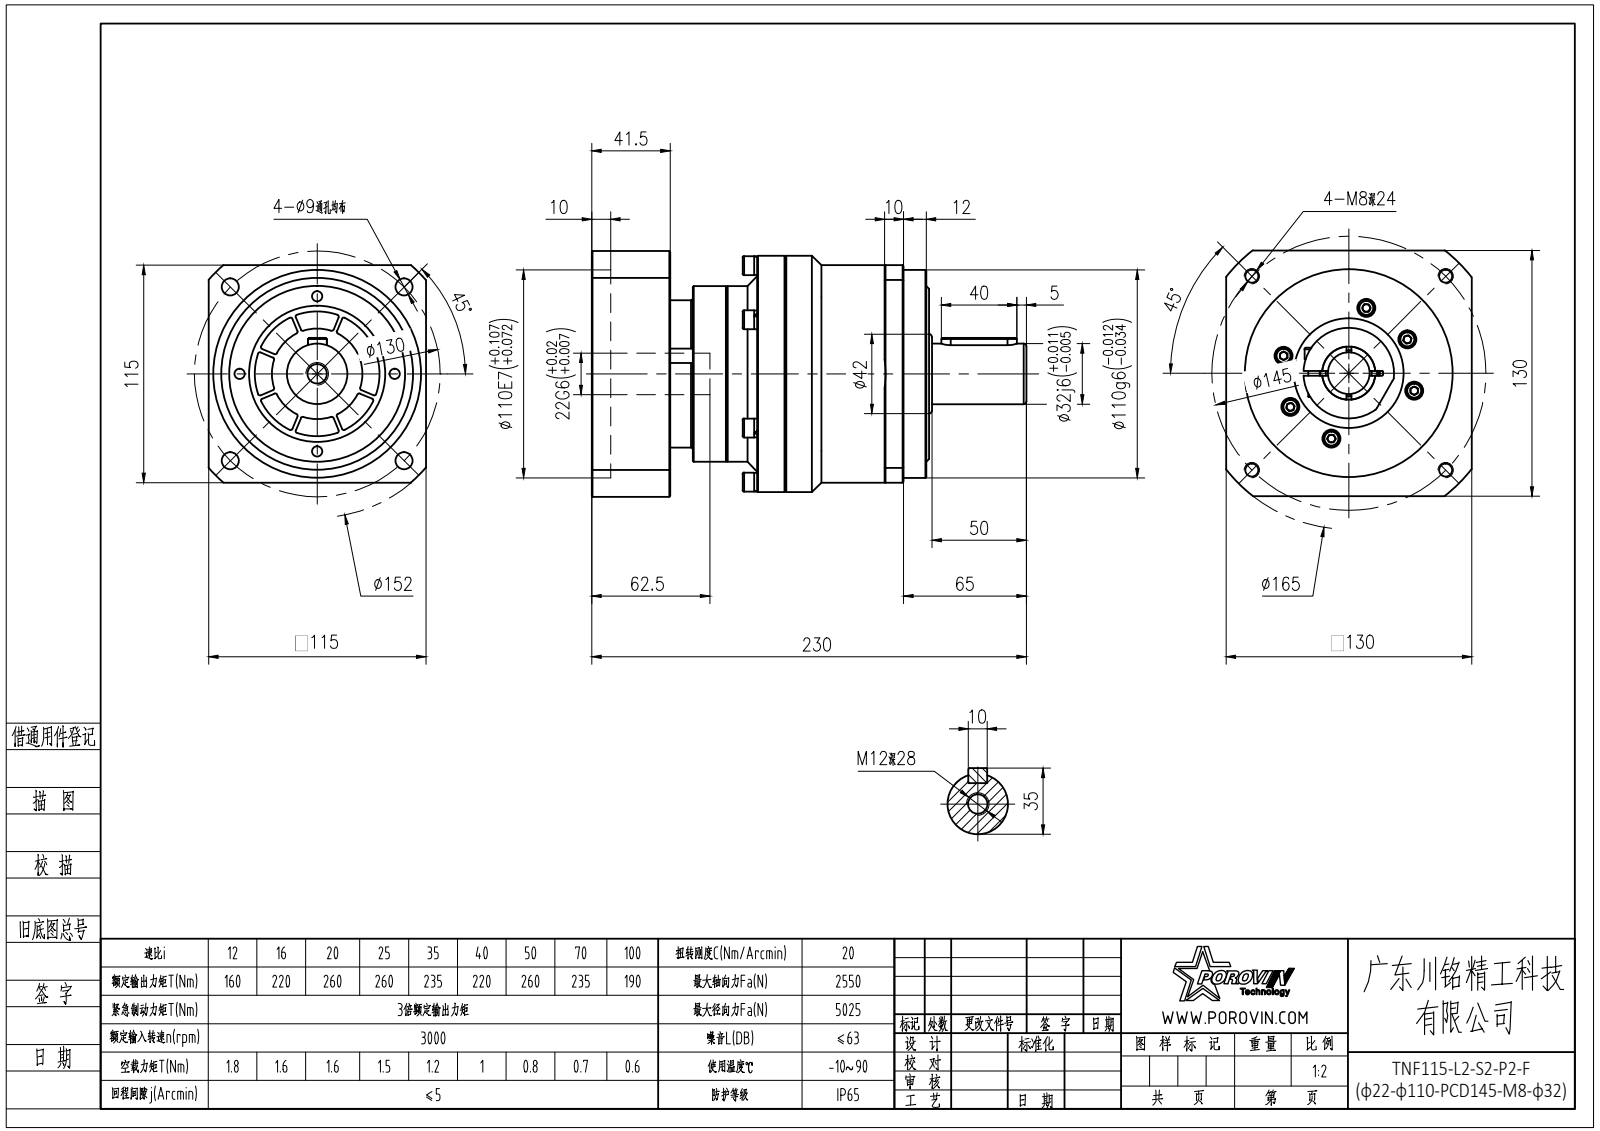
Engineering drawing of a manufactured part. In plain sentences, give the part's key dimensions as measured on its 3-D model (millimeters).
The part is named "hexagon socket head cap screws gb_GB_FASTENER_SCREWS_HSHCS M6X20-N; 一级齿圈加出轴 KS115 外形图; spring lock washers--normal type gb_GB_FASTENER_WASHER_SW 6; hexagon socket head cap screws gb_GB_FASTENER_SCREWS_HSHCS M6X25-N (+4 more)". Its 3-D file was written by "SolidWorks 2016 (CONFIG_CONTROL_DESIGN)". It is 41 solids with 1135 faces: 472 planar, 412 cylindrical and 251 other. Overall it measures 230 by 130 by 130 millimeters. Its volume is 1 633 000 cubic millimeters and its surface area 228 304 square millimeters. Round holes: 14 of diameter 5.5, 12 of diameter 4.2, 10 of diameter 5.4, 10 of diameter 9.5, 6 of diameter 6.6, 6 of diameter 6.68, 4 of diameter 6.8, 4 of diameter 9, 2 of diameter 10.2, 1 of diameter 5, 1 of diameter 6.5, 1 of diameter 13. Round bosses or shafts: 10 of diameter 8.5, 10 of diameter 8, 10 of diameter 5, 7 of diameter 10, 7 of diameter 6, 6 of diameter 9.88, 1 of diameter 125, 1 of diameter 115. Partial cylindrical surfaces (rounded edges, fillets, slot ends): 32 of radius 1, 2 of radius 5, 1 of radius 5.5, 1 of radius 76, 1 of radius 82.5. The main face-to-face distances are 61, 130, 31, 30, 102.5, 71.5, 41.5, 51.5, 20, 82.5. The hole center spacings are 46.18, 52.19, 97.37, 98.8, 105.99, 35.75, 40.75, 57.25.
